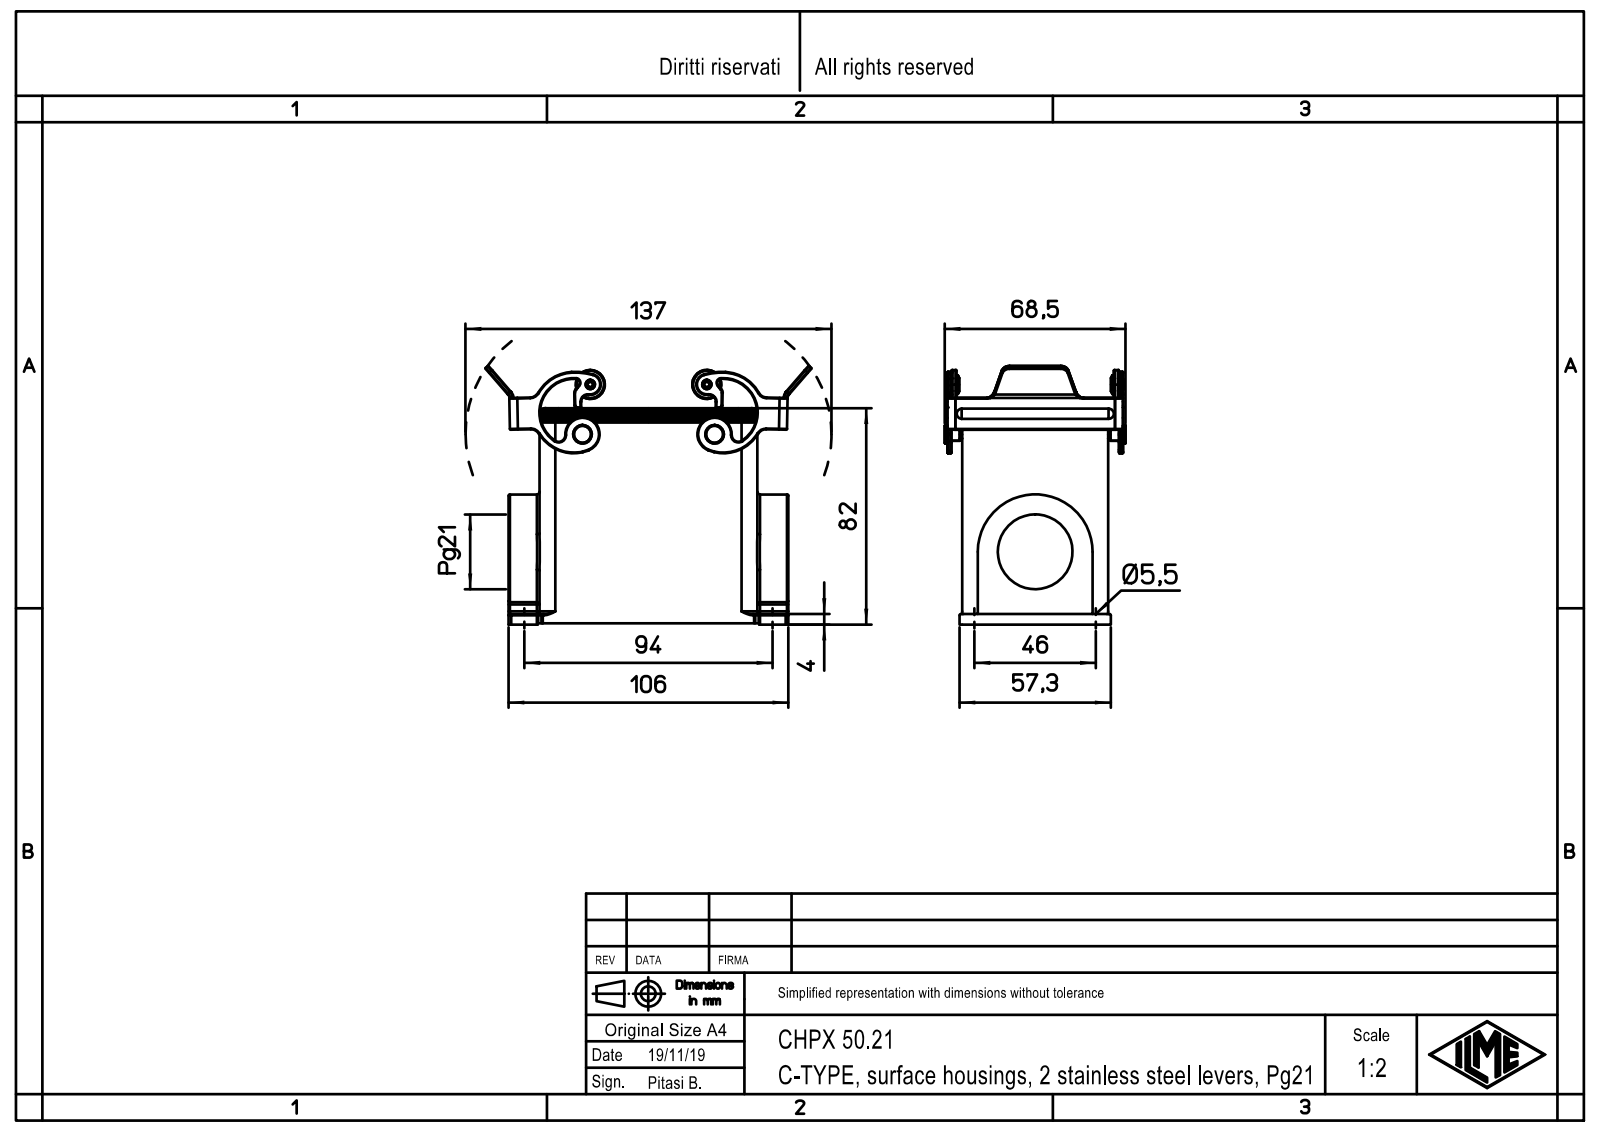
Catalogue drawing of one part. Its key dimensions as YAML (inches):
part_name: "Leva; CHPX 50.21; Leva.1; CHPX 50-21.stp"
step_written_by: "Creo Elements/Direct Modeling 20.1B 02-Apr-2019 (C) Parametric Technology GmbH (AUTOMOTIVE_DESIGN)"
units: inches
bodies: {solids: 3, faces: 616, planar: 198, cylindrical: 314, other: 104}
overall_size: [4.834, 3.884, 2.697]
volume: 8.801
surface_area: 112.3
round_holes:
  - {diameter: 0.122, count: 10}
  - {diameter: 0.097, count: 8}
  - {diameter: 0.197, count: 4}
  - {diameter: 0.217, count: 4}
  - {diameter: 0.047, count: 2}
  - {diameter: 0.079, count: 2}
  - {diameter: 0.897, count: 1}
  - {diameter: 0.945, count: 1}
  - {diameter: 1.054, count: 1}
  - {diameter: 1.114, count: 1}
round_bosses_or_shafts:
  - {diameter: 0.276, count: 4}
  - {diameter: 0.189, count: 4}
  - {diameter: 0.118, count: 4}
  - {diameter: 0.433, count: 2}
  - {diameter: 0.138, count: 2}
  - {diameter: 1.713, count: 1}
partial_cylinders:
  - {radius: 0.039, count: 24}
  - {radius: 0.118, count: 16}
  - {radius: 0.02, count: 14}
  - {radius: 0.059, count: 14}
  - {radius: 0.157, count: 8}
  - {radius: 0.138, count: 6}
  - {radius: 0.079, count: 4}
  - {radius: 0.098, count: 4}
face_to_face_distances: [0.118, 2.059, 2.177, 1.941, 0.433, 0.138, 0.059, 2.815, 2.382, 0.315]
hole_center_spacings: [0.564, 0.63, 0.929, 0.945, 1.197, 1.78, 2.598, 2.674]
